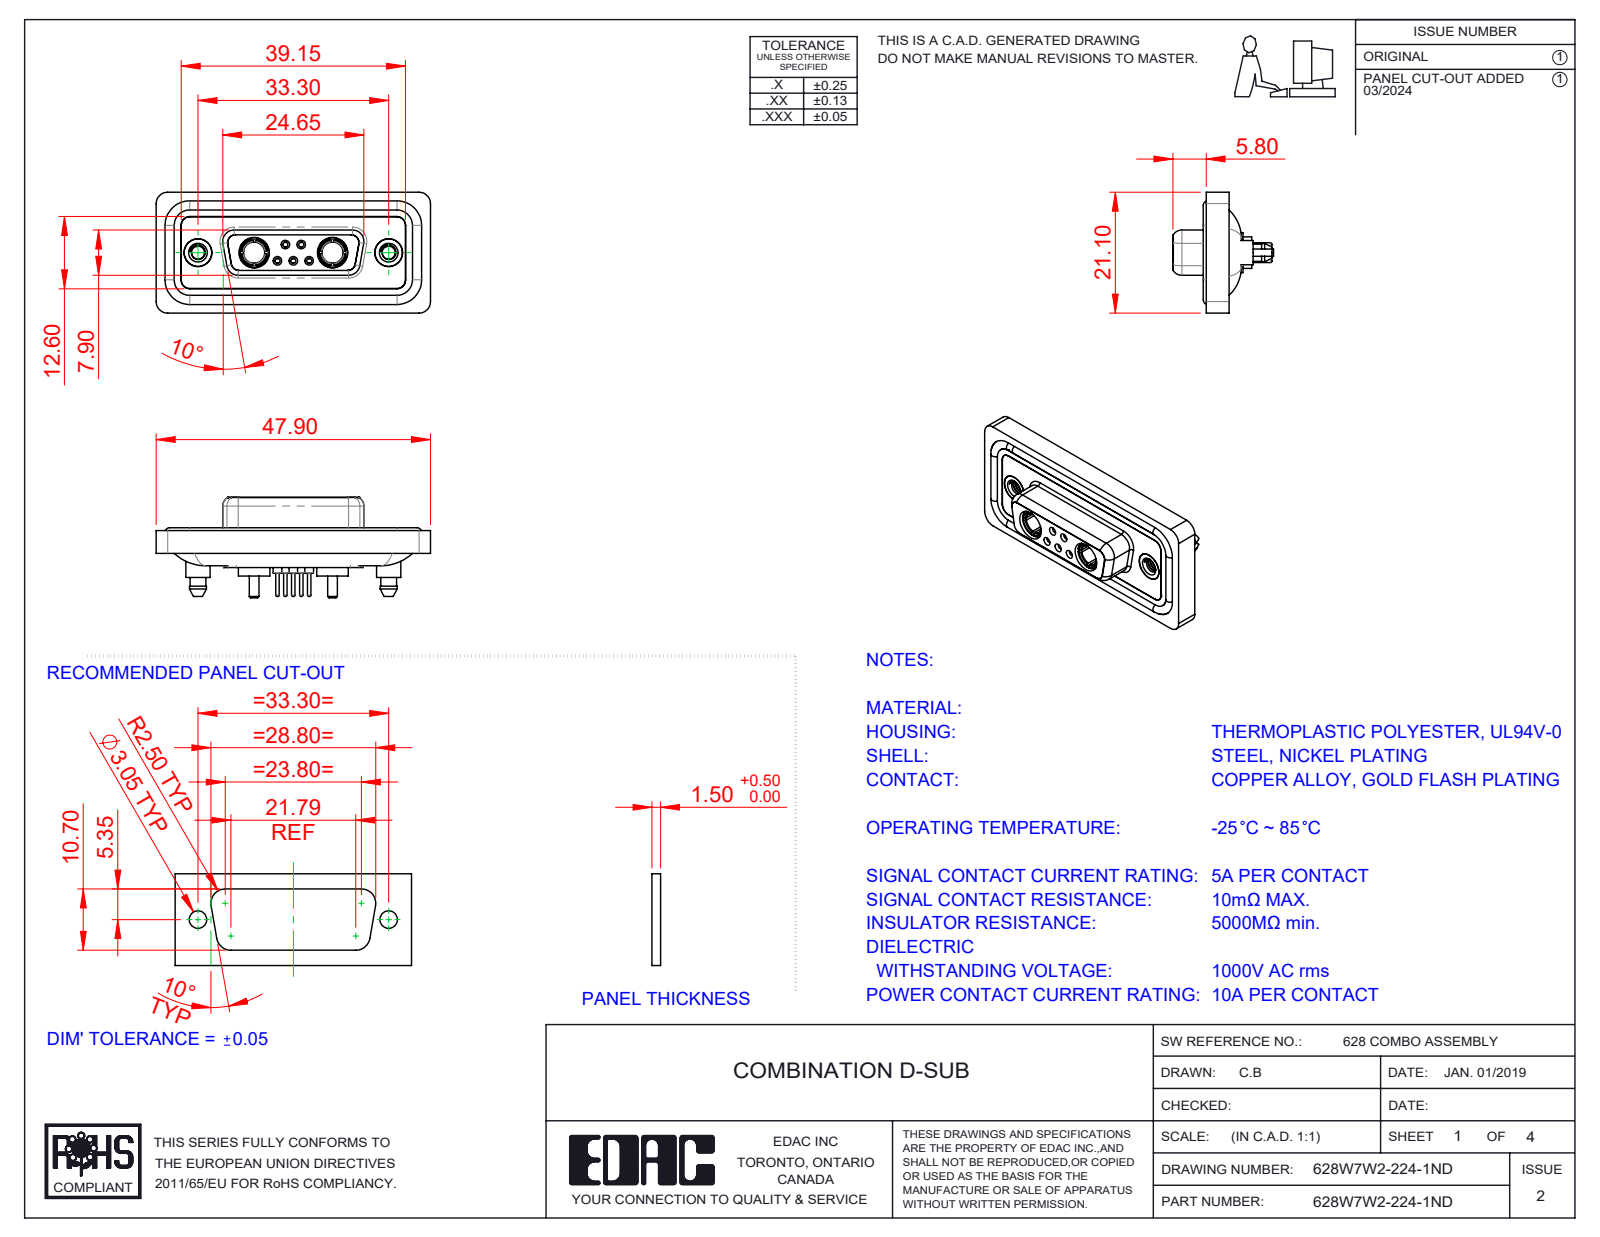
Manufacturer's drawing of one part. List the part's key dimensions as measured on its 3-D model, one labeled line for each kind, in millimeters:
Part name (STEP PRODUCT): 628Combo Contact Row 1_24; Power Socket_10A S; 628Combo Waterproof Housing_15 Contacts; 628W7W2-224-1ND (+5 more)
STEP written by: SolidWorks 2023 (CONFIG_CONTROL_DESIGN)
Units: millimetres
Bodies: 16 solids, 875 faces (254 planar, 377 cylindrical, 244 other)
Overall size (bounding box): 47.9 × 21.1 × 17.55
Volume: 6 183 mm³ · Surface area: 10 199 mm²
Round holes (diameter × count): ⌀0.9 ×5, ⌀1.1 ×5, ⌀1.5 ×5, ⌀2 ×5, ⌀4.85 ×4, ⌀1.6 ×3, ⌀1.7 ×2, ⌀2.26 ×2, ⌀3.7 ×2, ⌀4 ×2, ⌀4.05 ×2, ⌀5 ×2
Round bosses / shafts (diameter × count): ⌀1.6 ×6, ⌀2.2 ×5, ⌀0.6 ×5, ⌀5.5 ×2, ⌀5.4 ×2, ⌀5.2 ×2, ⌀4.96 ×2, ⌀4.95 ×2
Partial cylindrical surfaces — rounded edges, fillets, slot ends (radius × count): R1.5 ×24, R2 ×20, R1.35 ×12, R1.6 ×10, R0.25 ×4, R0.5 ×4, R0.6 ×4, R0.65 ×4
Main face-to-face distances: 0.4, 1.8, 1.6, 0.5, 2.9, 1.1, 7.45, 5.65, 6.6, 7.05
Hole centre spacings: 3.16, 2.77, 9.8, 23.5, 4.31, 4.33, 5.03, 5.04
